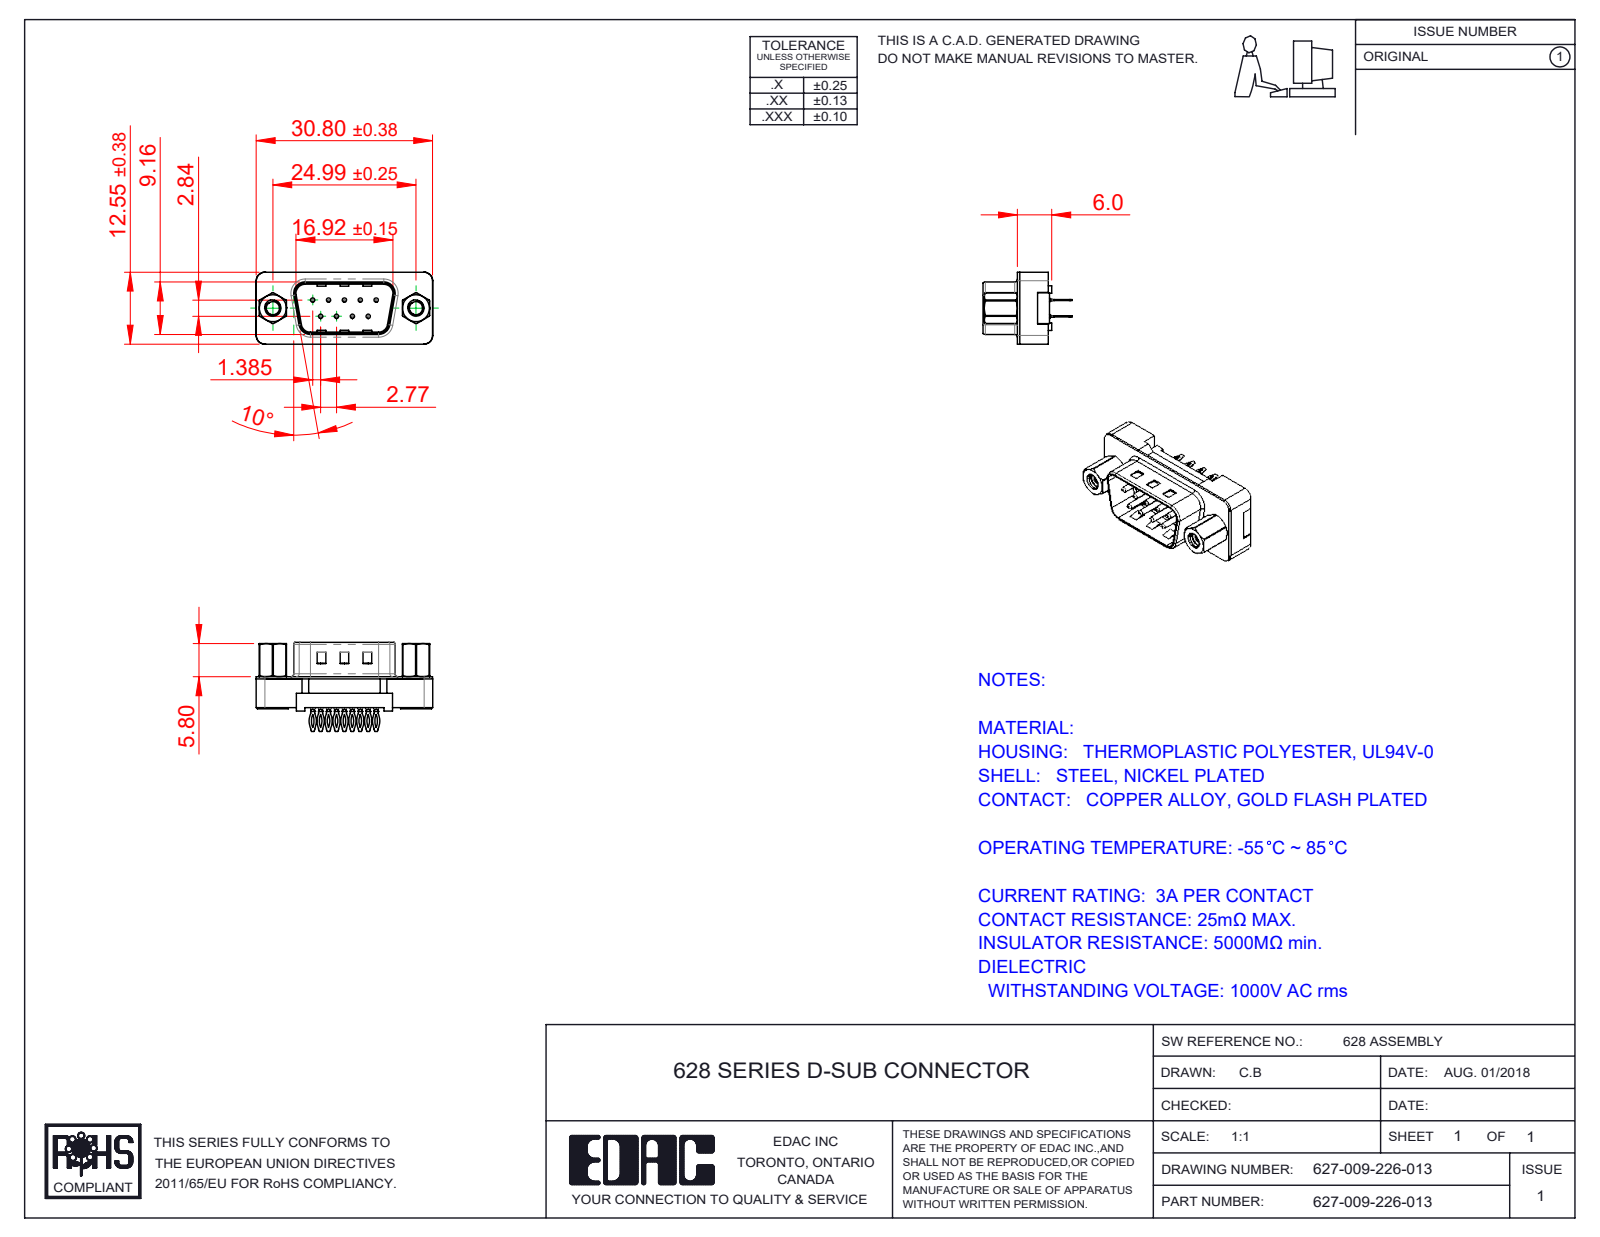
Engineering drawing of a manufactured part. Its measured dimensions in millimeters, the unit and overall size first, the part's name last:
Units: millimetres
Overall size (bounding box): 30.81 × 15.55 × 12.55
Round holes (diameter × count): ⌀0.35 ×9, ⌀0.85 ×9, ⌀2.26 ×2, ⌀2.29 ×2, ⌀4 ×2, ⌀4.8 ×2, ⌀5 ×2
Round bosses / shafts (diameter × count): ⌀0.75 ×9, ⌀4.9 ×2, ⌀2.79 ×2
Partial cylindrical surfaces — rounded edges, fillets, slot ends (radius × count): R0.25 ×18, R2.92 ×18, R3.33 ×18, R0.12 ×9, R0.5 ×8, R1.5 ×7, R0.9 ×4, R1.6 ×4
Main face-to-face distances: 0.4, 2.5, 5.4, 5, 2.9, 8.76, 2.1, 2.38, 6.5, 0.68
Hole centre spacings: 3.16, 2.77, 5.04, 5.54, 7.49, 5.03, 7.09, 8.31
Volume: 1 858 mm³ · Surface area: 3 838 mm²
Bodies: 15 solids, 1026 faces (548 planar, 348 cylindrical, 130 other)
Part name (STEP PRODUCT): 627 PB Contact Row 1_26; 627 PB Shell_09 Contacts; 627 4-40 Hex Standoff; 627 PB Contact Row 2_26 (+3 more)
STEP written by: SolidWorks 2020 (CONFIG_CONTROL_DESIGN)
